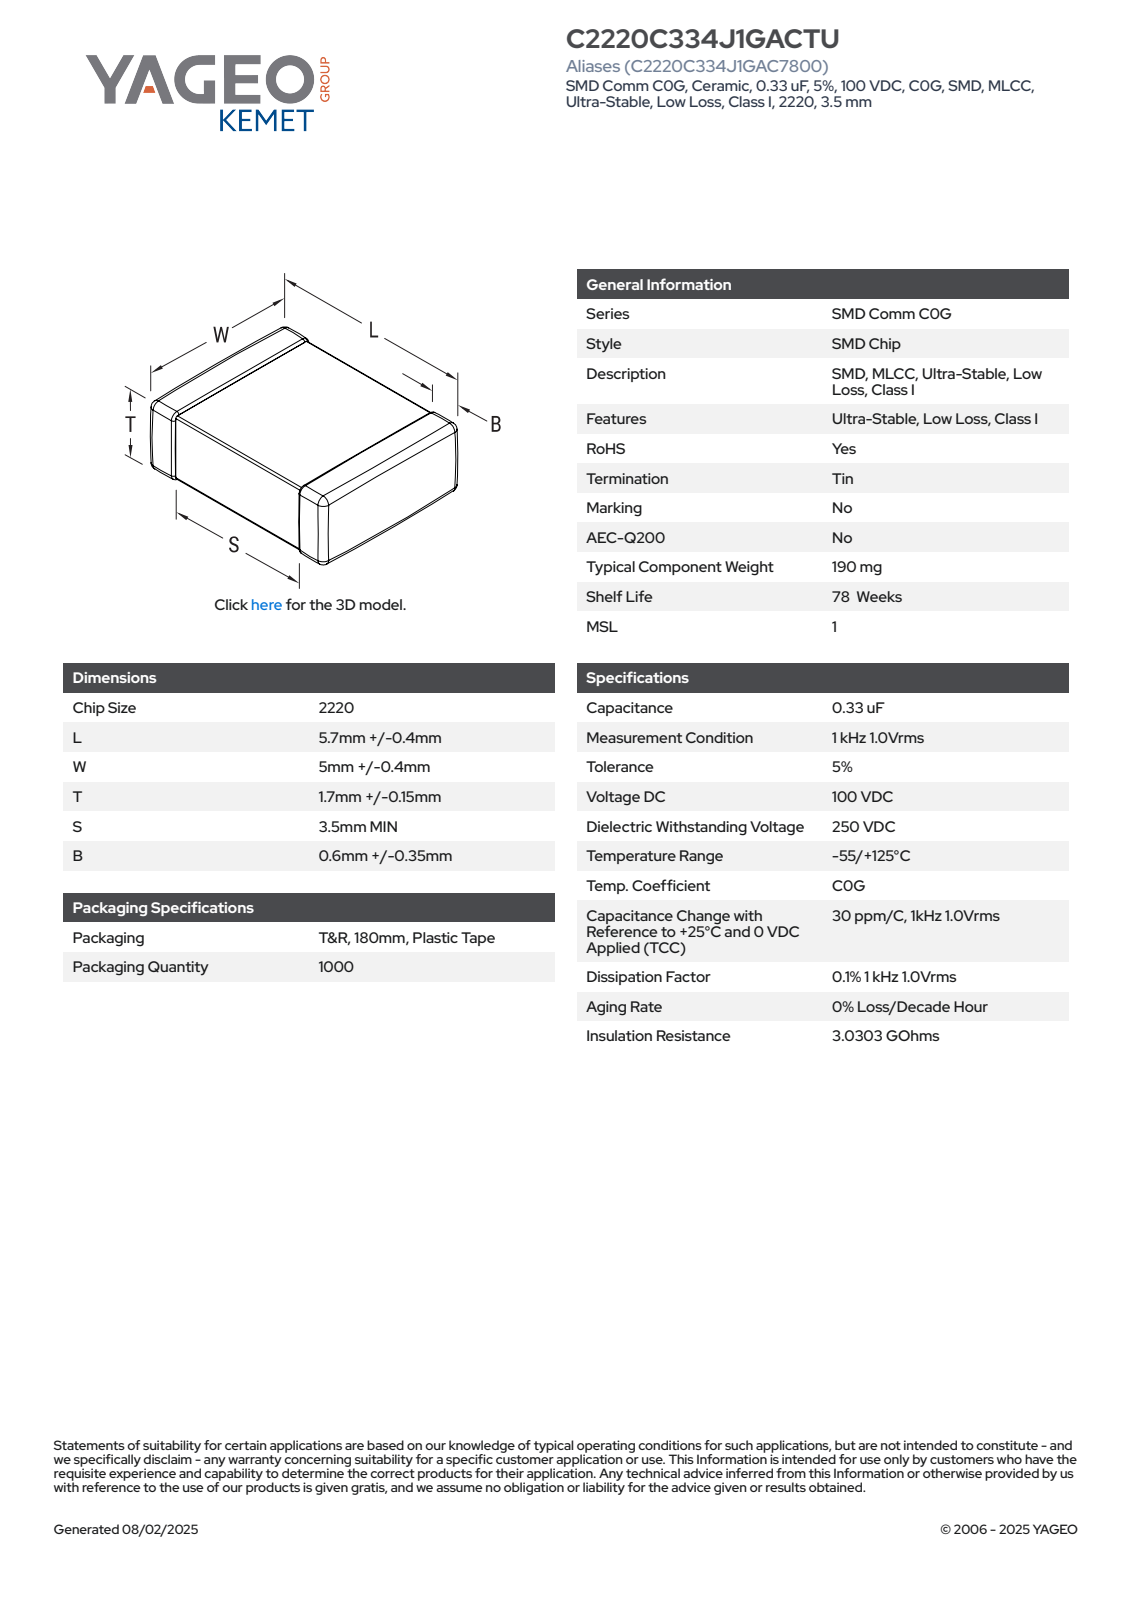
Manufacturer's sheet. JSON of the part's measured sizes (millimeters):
{"part_name": "CCS_CCSTDNOS_2220_L6.1W5.4T1.85B0.95", "step_written_by": "SolidWorks 2014 (AUTOMOTIVE_DESIGN)", "units": "millimeters", "bodies": {"solids": 4, "faces": 125, "planar": 71, "cylindrical": 38, "other": 16}, "overall_size": [6.1, 5.4, 1.85], "volume_mm3": 54, "surface_area_mm2": 105, "partial_cylinders_radius": [[0.11, 24]], "face_to_face_distances": [1.63, 1.74, 6.1, 1.85, 5.18, 5.29, 5.4, 2.66, 2.74, 2.55]}
